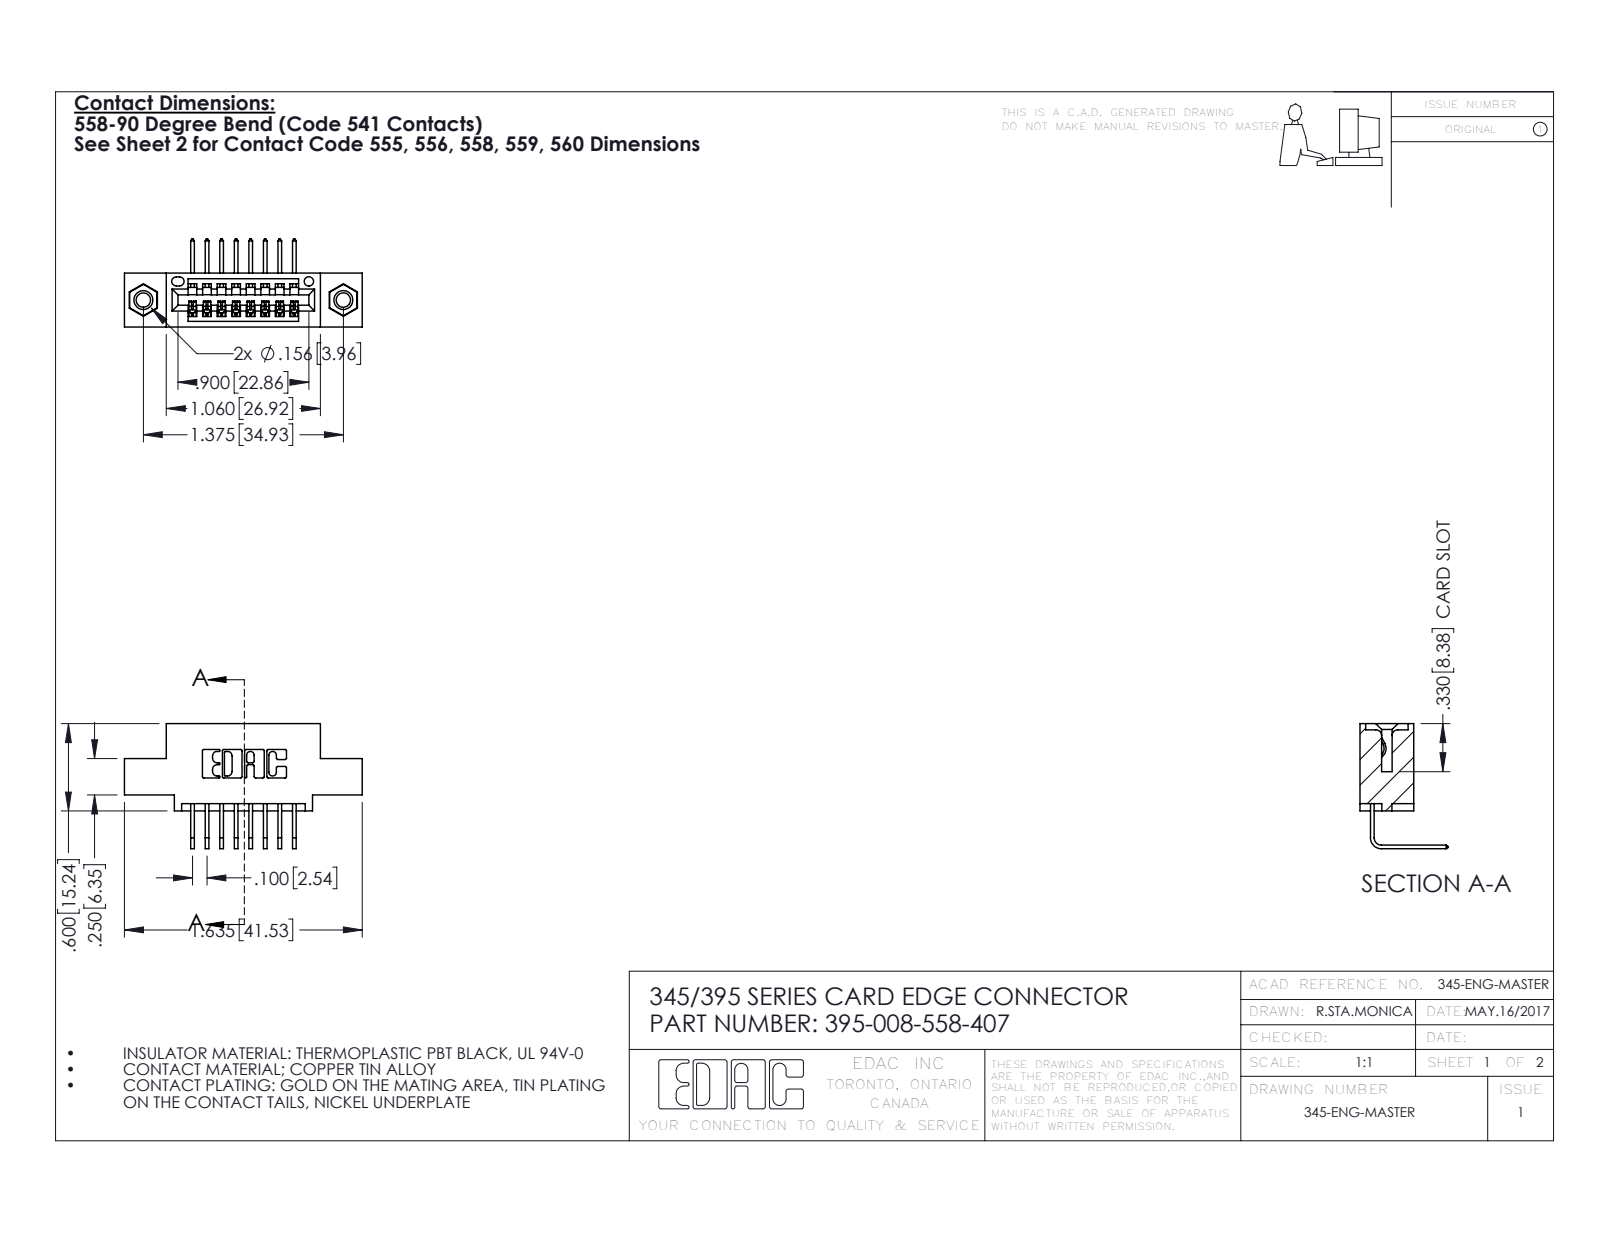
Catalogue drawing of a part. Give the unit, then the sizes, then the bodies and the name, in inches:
Units: inches
Overall size (bounding box): 1.635 × 0.859 × 0.605
Round holes (diameter × count): ⌀0.098 ×2, ⌀0.125 ×2, ⌀0.156 ×2, ⌀0.064 ×1
Round bosses / shafts (diameter × count): ⌀0.155 ×2
Partial cylindrical surfaces — rounded edges, fillets, slot ends (radius × count): R0.01 ×22, R0.006 ×16, R0.007 ×6, R0.031 ×6, R0.026 ×3, R0.031 ×2, R0.04 ×2, R0.014 ×1
Main face-to-face distances: 0.2, 0.37, 0.1, 0.072, 0.298, 0.3, 0.16, 0.098, 0.272, 0.025
Hole centre spacings: 0.27, 1.144, 1.375
Volume: 0.22 in³ · Surface area: 7.131 in²
Bodies: 11 solids, 670 faces (452 planar, 202 cylindrical, 16 other)
Part name (STEP PRODUCT): 345-292-001_558 Tail - 2; 395-008-558-407; 345 Part_0.110 Offset - 0.156 Dia-TI; 345-250-001_345-250-005-103
STEP written by: SolidWorks 2016 (CONFIG_CONTROL_DESIGN)
